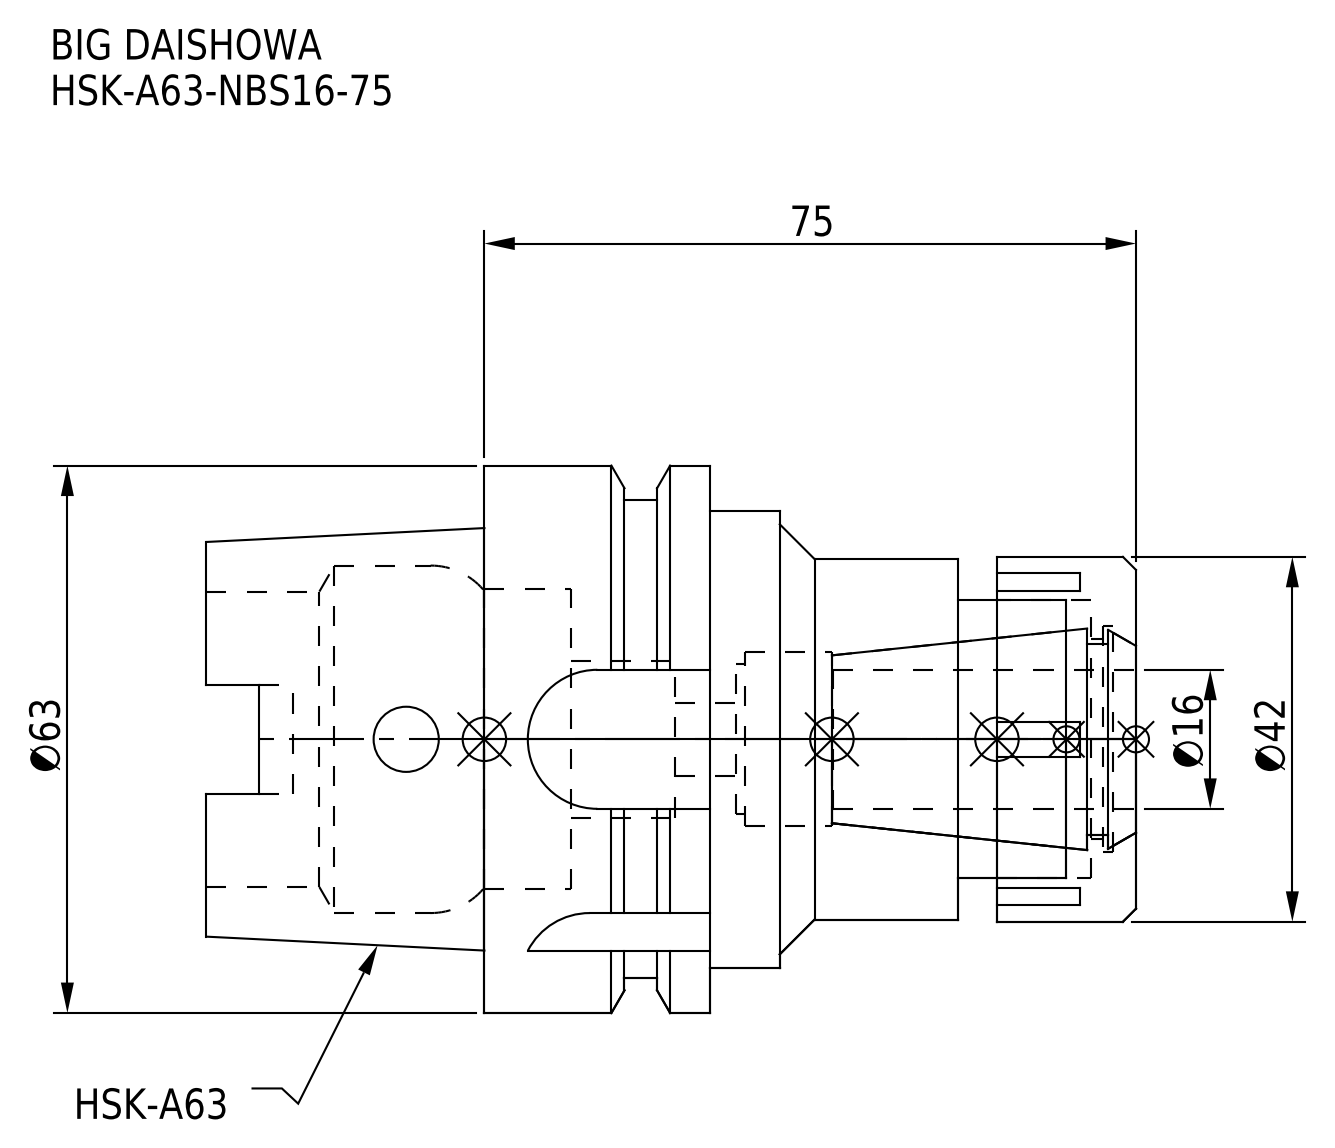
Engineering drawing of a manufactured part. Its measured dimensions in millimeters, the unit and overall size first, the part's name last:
Units: millimetres
Overall size (bounding box): 107 × 63 × 63
Round holes (diameter × count): ⌀7.5 ×1, ⌀8.4 ×1, ⌀17.3 ×1, ⌀18 ×1, ⌀20 ×1, ⌀23 ×1, ⌀26 ×1, ⌀32 ×1, ⌀34 ×1, ⌀34.5 ×1, ⌀40 ×1
Round bosses / shafts (diameter × count): ⌀63 ×1, ⌀55 ×1, ⌀52.6 ×1, ⌀42 ×1, ⌀41.5 ×1
Partial cylindrical surfaces — rounded edges, fillets, slot ends (radius × count): R2.88 ×4, R8 ×4
Main face-to-face distances: 8, 26, 75, 20.5, 49, 33, 65.05, 16.05, 9.95, 41
Volume: 134 405 mm³ · Surface area: 35 720 mm²
Bodies: 2 solids, 141 faces (70 planar, 49 cylindrical, 22 other)
Part name (STEP PRODUCT): HA63NB16075-160_ASM.stp; HSK-A63-NBS16-75; DXF_TEMP_ASSY_ASM_4_ASM.stp; HSK-A63-NBS16-75_1.stp (+3 more)
STEP written by: SolidWorks 2019 (CONFIG_CONTROL_DESIGN)
